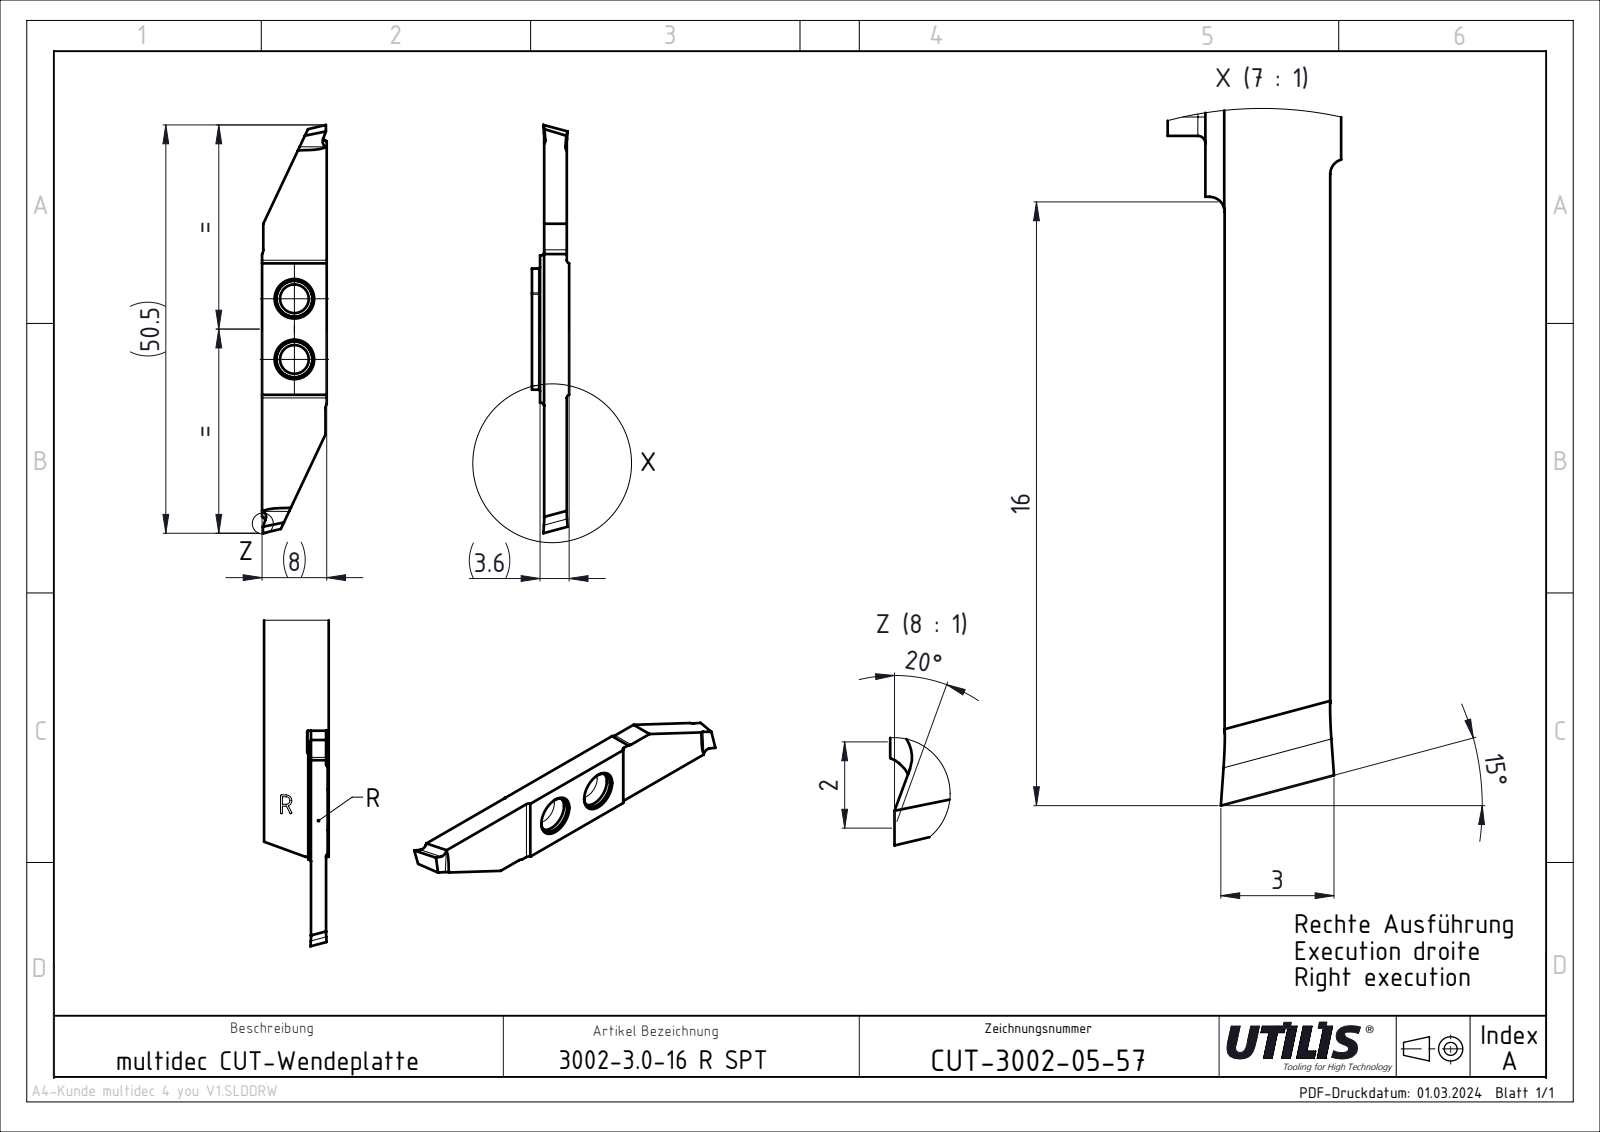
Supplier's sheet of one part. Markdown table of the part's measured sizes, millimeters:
| quantity | value |
| --- | --- |
| part name | CUT-3002 SPT Slim_and_Deep; ASME Y14.5 |
| STEP written by | SolidWorks 2023 SP4 \|\| FormatWorks Professional (AP242_MANAGED_MODEL_BASED_3D_ENGINEERING_MIM_LF) |
| units | millimeters |
| bodies | 1 solid, 32 faces (22 planar, 10 cylindrical, 0 other) |
| overall size | 50.5 × 8 × 3.6 |
| volume | 953 mm³ |
| surface area | 1 019 mm² |
| round holes (diameter × count) | 3.55 × 2 |
| partial cylindrical surfaces (radius × count) | 0.4 × 4, 1 × 2 |
| main face-to-face distances | 2.8, 3.09, 0.51, 3.31, 3.6, 8, 18.09, 7.85, 0.41, 7.7 |
| hole center spacings | 7.5 |
